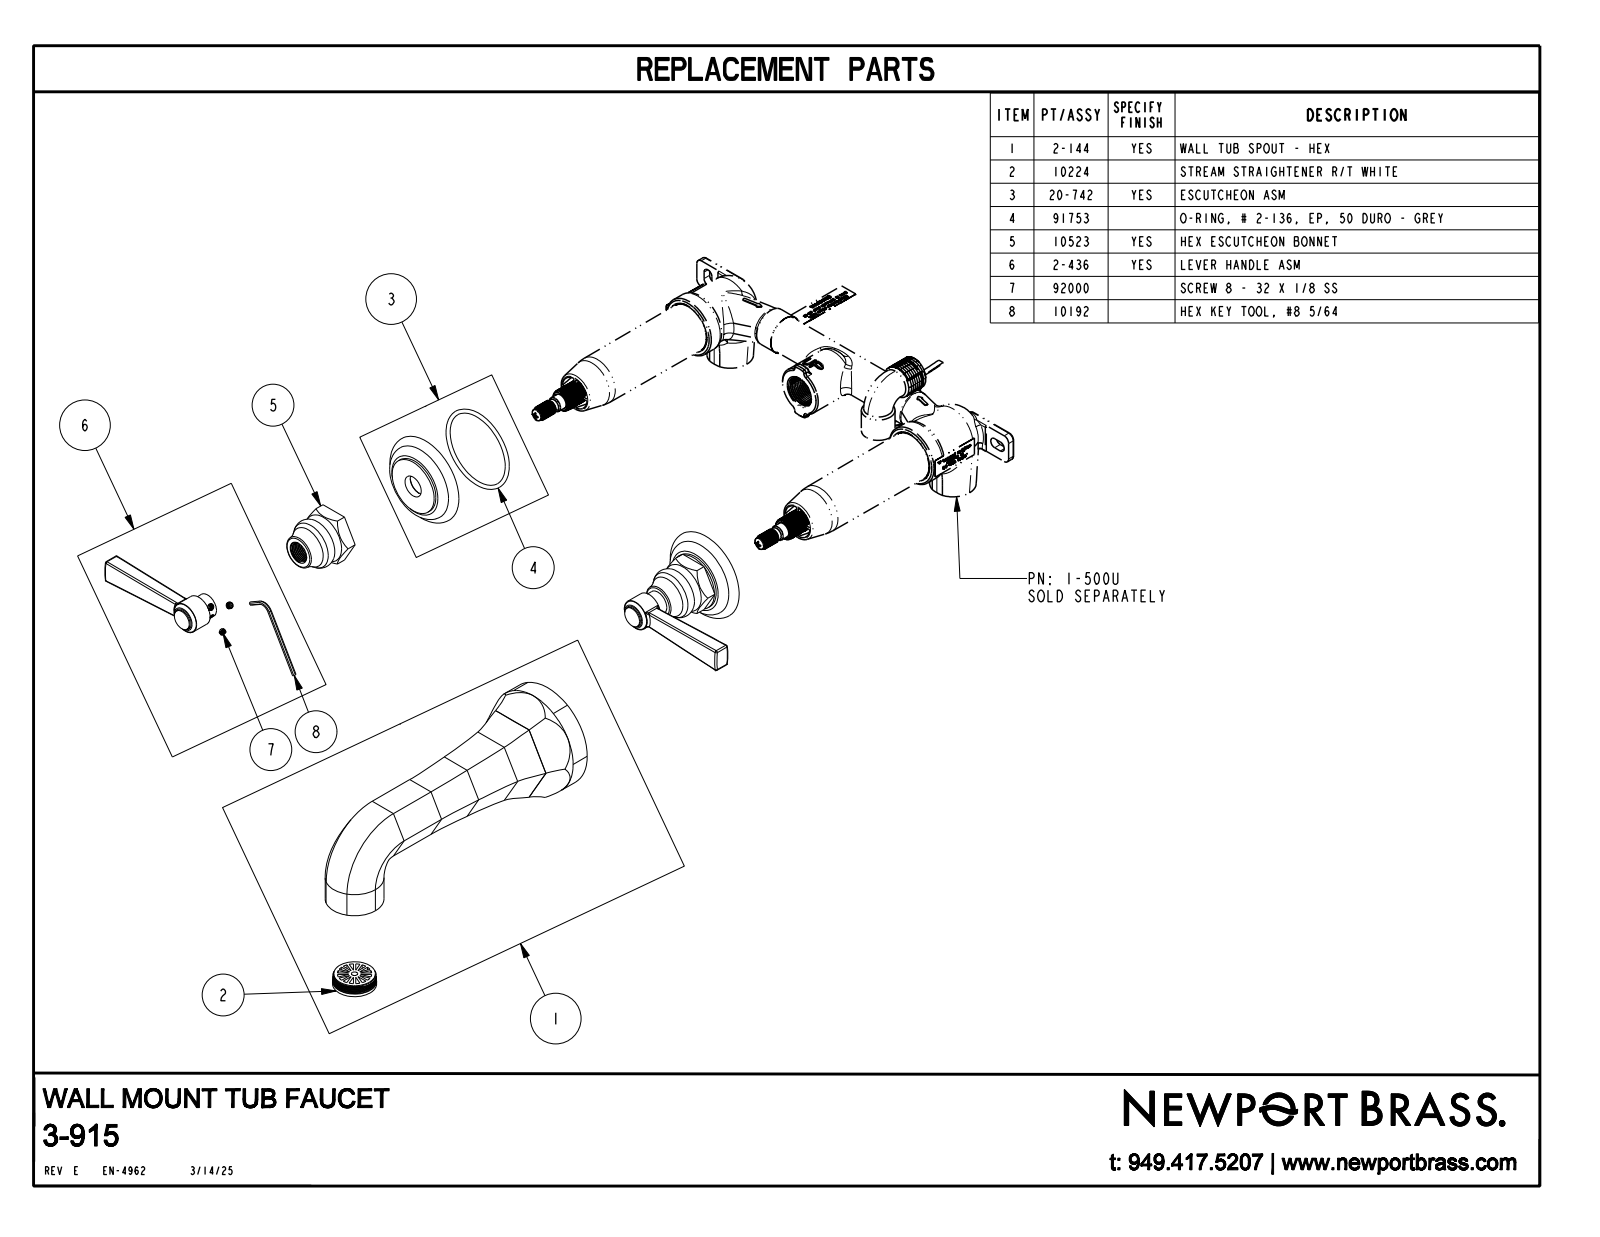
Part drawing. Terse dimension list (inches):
name: 3-915_SW0001
written by: CREO PARAMETRIC BY PTC INC, 2018400 (AUTOMOTIVE_DESIGN)
unit: in
bodies: 3 solids, 238 faces (64 planar, 36 cylindrical, 138 other)
size: 13.574 × 8.825 × 7.562
volume: 26.17 in³; area: 94.87 in²
bosses: 2× ⌀1.482, 2× ⌀0.8, 2× ⌀0.625, 2× ⌀0.525, 1× ⌀2.8
rounds: 6× R2.125, 4× R0.04, 4× R0.055
face distances: 1.299, 0.124, 0.995, 2.294, 3.937, 1.313, 0.375, 2.624, 5.25, 7.874
